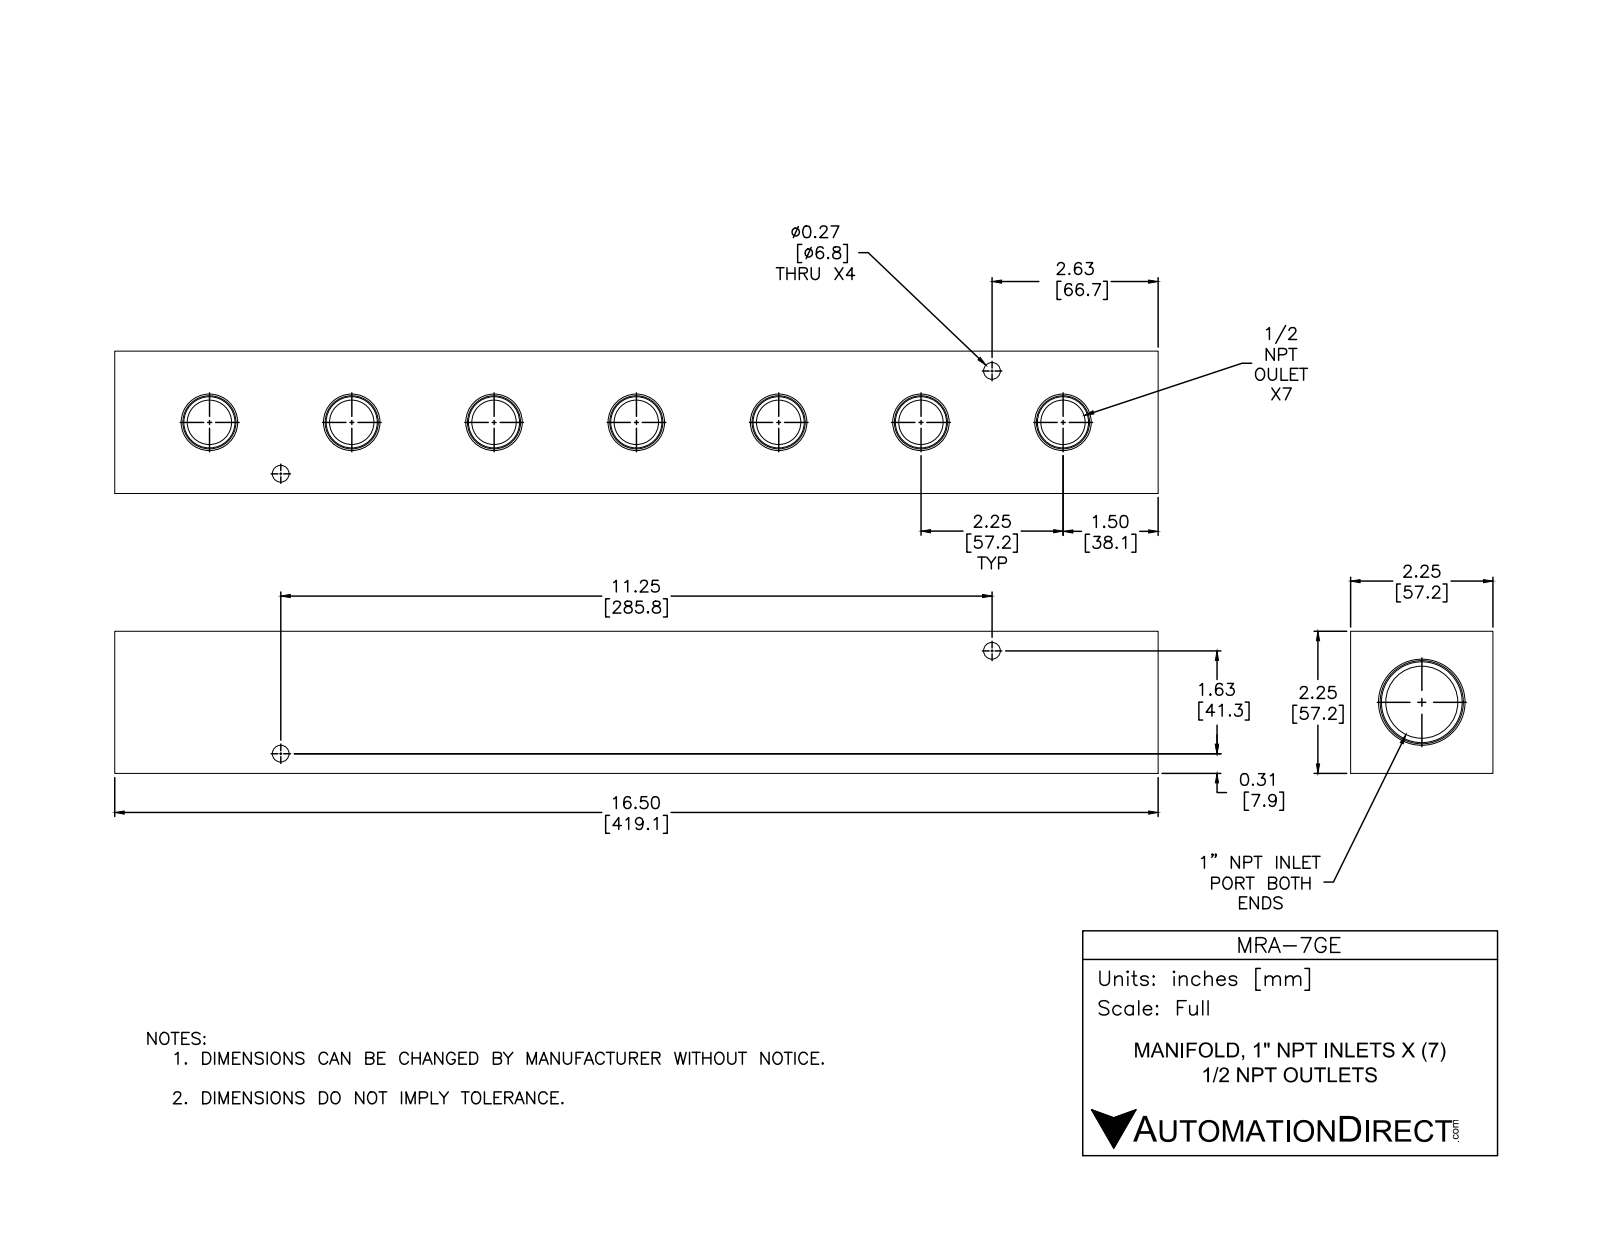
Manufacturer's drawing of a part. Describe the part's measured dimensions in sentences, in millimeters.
The part is named "MRA-7GE". Its 3-D file was written by "SolidWorks 2015 (CONFIG_CONTROL_DESIGN)". It is 1 solid with 83 faces: 15 planar, 32 cylindrical and 36 other. Overall it measures 419.1 by 57.2 by 57.2 millimeters. Its volume is 1 043 000 cubic millimeters and its surface area 146 700 square millimeters. Round holes: 7 of diameter 17.9, 4 of diameter 6.8, 1 of diameter 29. The main face-to-face distances are 57.2, 419.1, 43.7, 13.5, 16.8, 402.3, 385.6. The hole center spacings are 57.2, 114.3, 35.3, 171.5, 228.6, 88.2, 144.3, 201.1.
